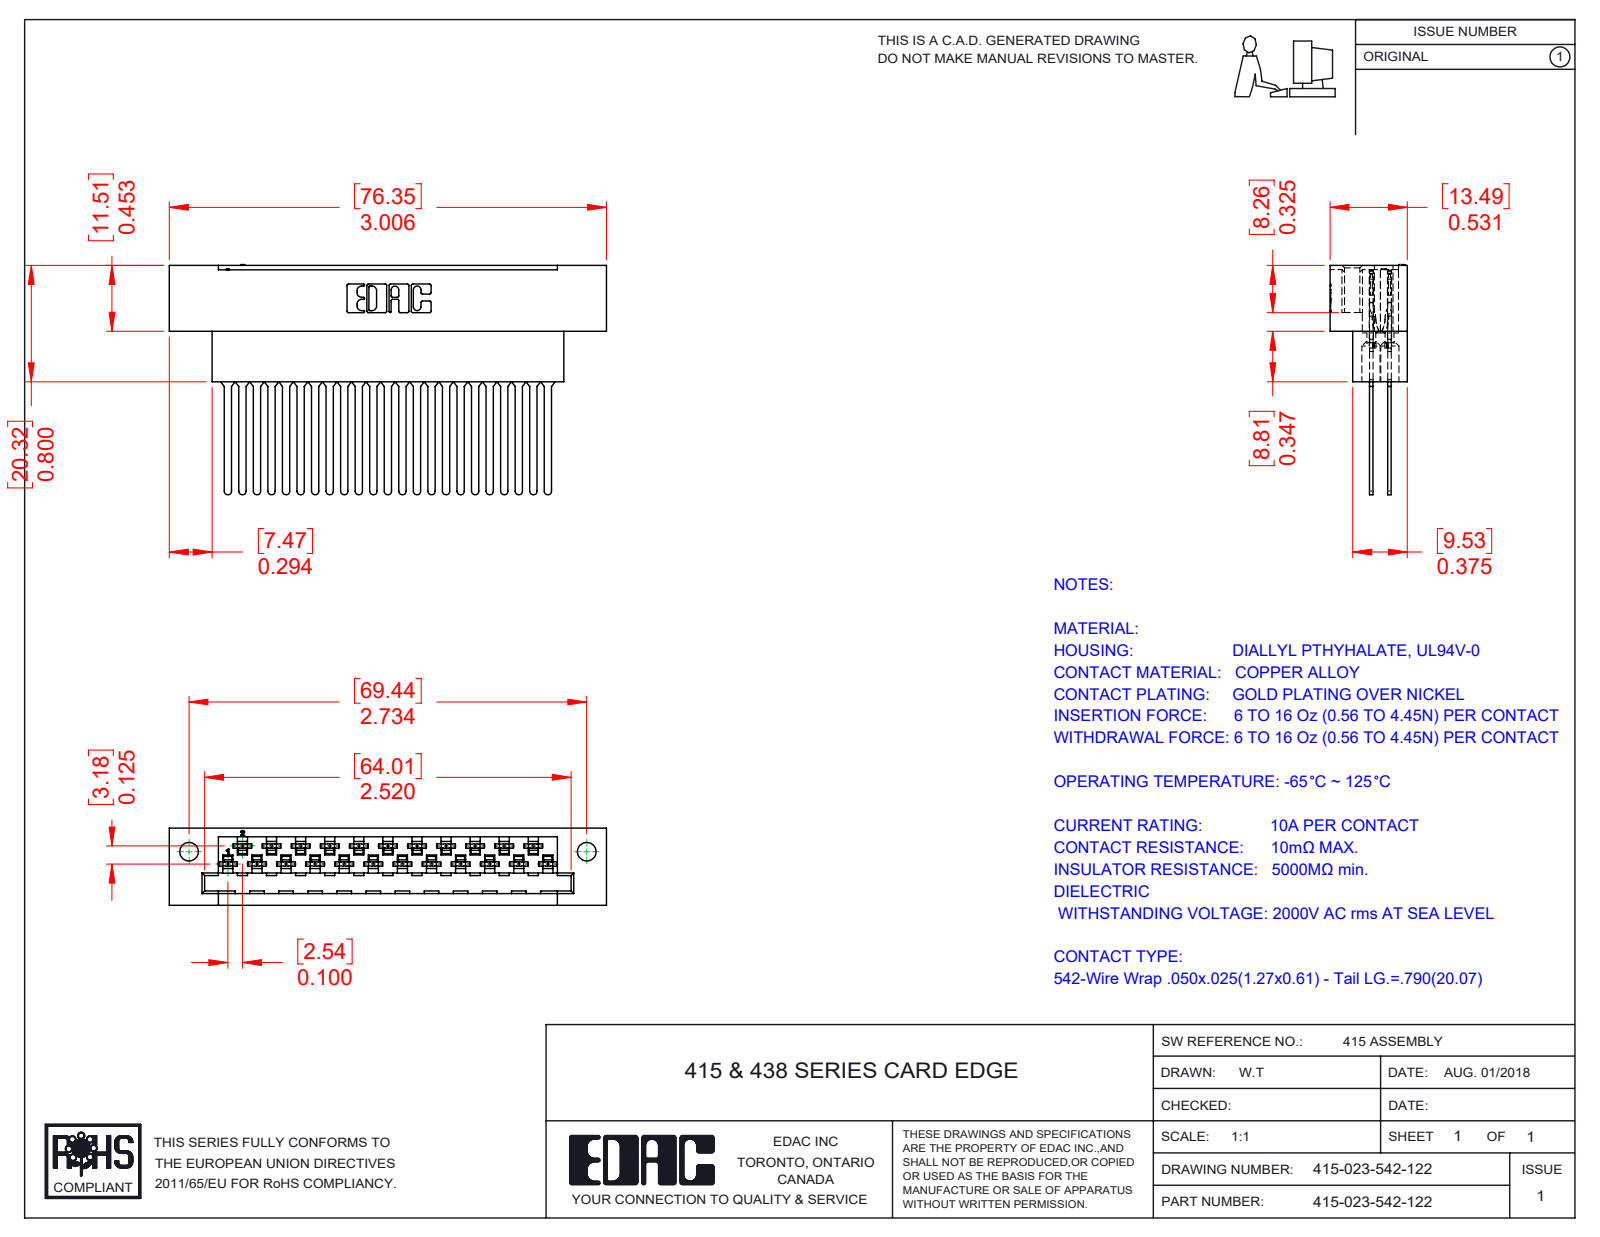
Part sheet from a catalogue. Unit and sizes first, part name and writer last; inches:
Units: inches
Overall size (bounding box): 3.006 × 1.581 × 0.531
Round holes (diameter × count): ⌀0.05 ×23, ⌀0.13 ×23, ⌀0.128 ×2
Partial cylindrical surfaces — rounded edges, fillets, slot ends (radius × count): R0.012 ×92, R0.022 ×92, R0.007 ×46, R0.008 ×46, R0.016 ×46, R0.08 ×46, R0.025 ×23, R0.01 ×22
Main face-to-face distances: 0.125, 0.024, 0.295, 0.531, 0.26, 0.236, 0.271, 0.05, 0.074, 0.111
Hole centre spacings: 0.2, 0.4, 0.6, 0.8, 1, 0.1, 0.16, 1.2
Volume: 0.774 in³ · Surface area: 25.7 in²
Bodies: 24 solids, 2398 faces (1527 planar, 642 cylindrical, 229 other)
Part name (STEP PRODUCT): 516-290-001_542; 415-210-001_415-210-023-122; 415-023-542-122
STEP written by: SolidWorks 2016 (CONFIG_CONTROL_DESIGN)
